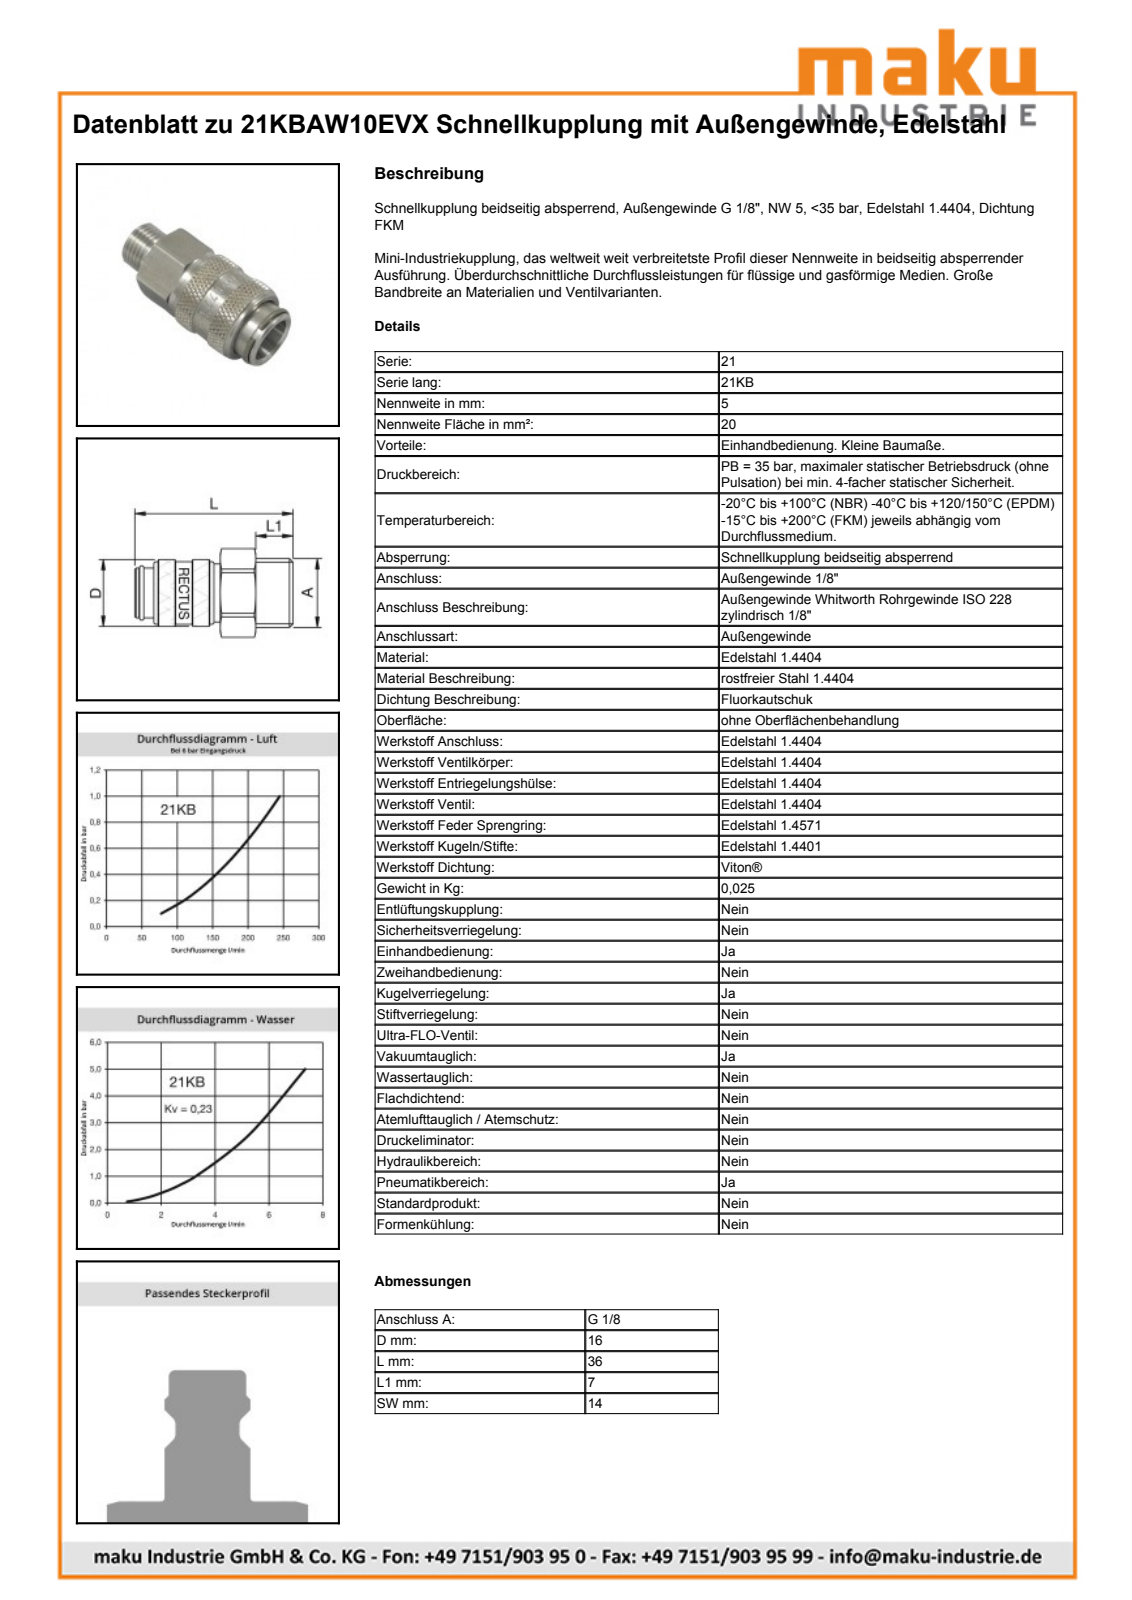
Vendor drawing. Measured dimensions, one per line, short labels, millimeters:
name: D105878
written by: Autodesk Inventor 2011 (AUTOMOTIVE_DESIGN)
unit: mm
bodies: 2 solids, 398 faces (162 planar, 63 cylindrical, 173 other)
size: 36.15 × 16.15 × 16.15
volume: 5 171 mm³; area: 3 376 mm²
holes: 1× ⌀12.15, 1× ⌀14
bosses: 1× ⌀16.15, 1× ⌀15.1, 1× ⌀12, 1× ⌀11.4, 1× ⌀11.15, 1× ⌀9.73
rounds: 1× R7.45, 1× R7.9
face distances: 14, 29.15, 36.15, 7, 11.55, 16.15, 13, 20, 4.6, 24.55
